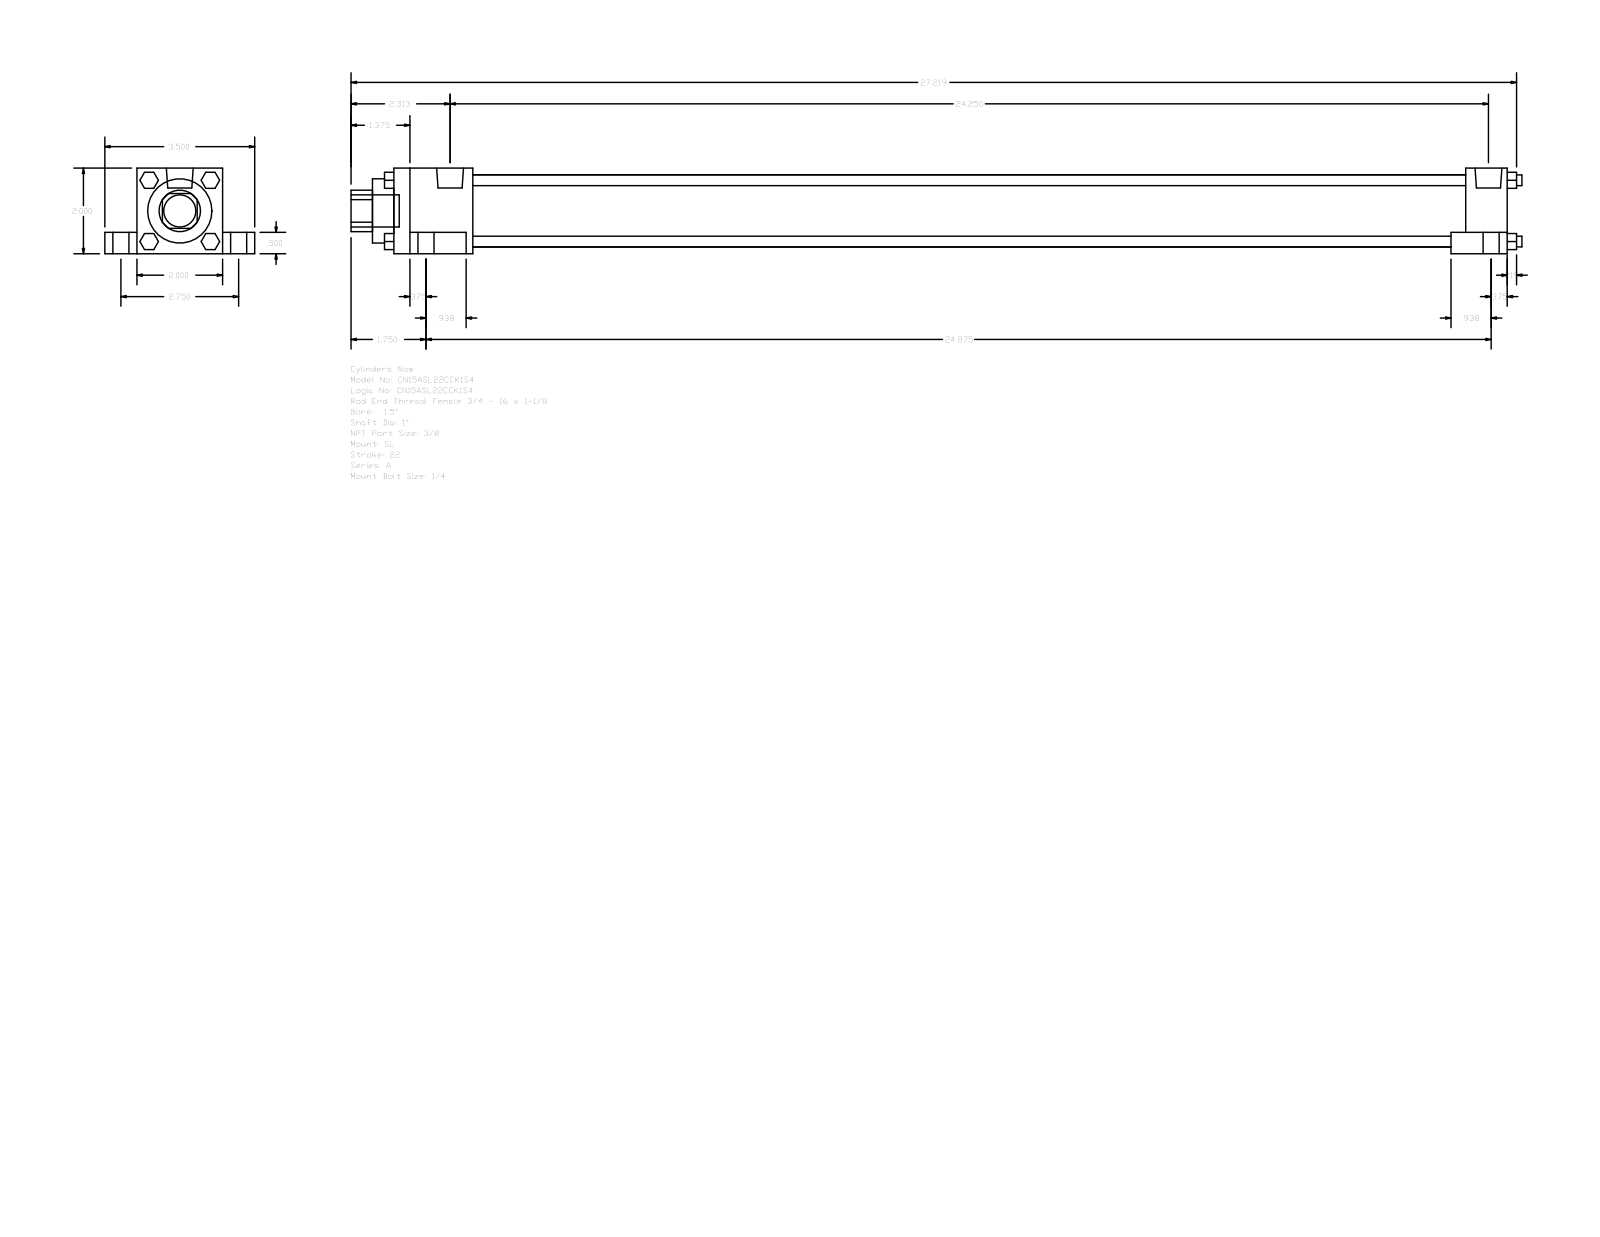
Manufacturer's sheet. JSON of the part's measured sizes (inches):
{"part_name": "A_SL__0150_1", "step_written_by": "GSSL Pune (CONFIG_CONTROL_DESIGN)", "units": "inches", "bodies": {"solids": 0, "faces": 148, "planar": 112, "cylindrical": 36, "other": 0}, "overall_size": [27.344, 3.5, 2], "round_holes": [[1, 1], [1.5, 1], [1.69, 1]], "round_bosses_or_shafts": [[0.625, 4], [0.375, 4], [0.25, 4], [0.219, 4], [0.627, 2], [0.75, 1]], "partial_cylinders_radius": [[0.484, 1]], "face_to_face_distances": [2, 0.5, 1.5, 0.75, 2.75, 0.375, 26, 1.313, 25.031, 0.969]}
